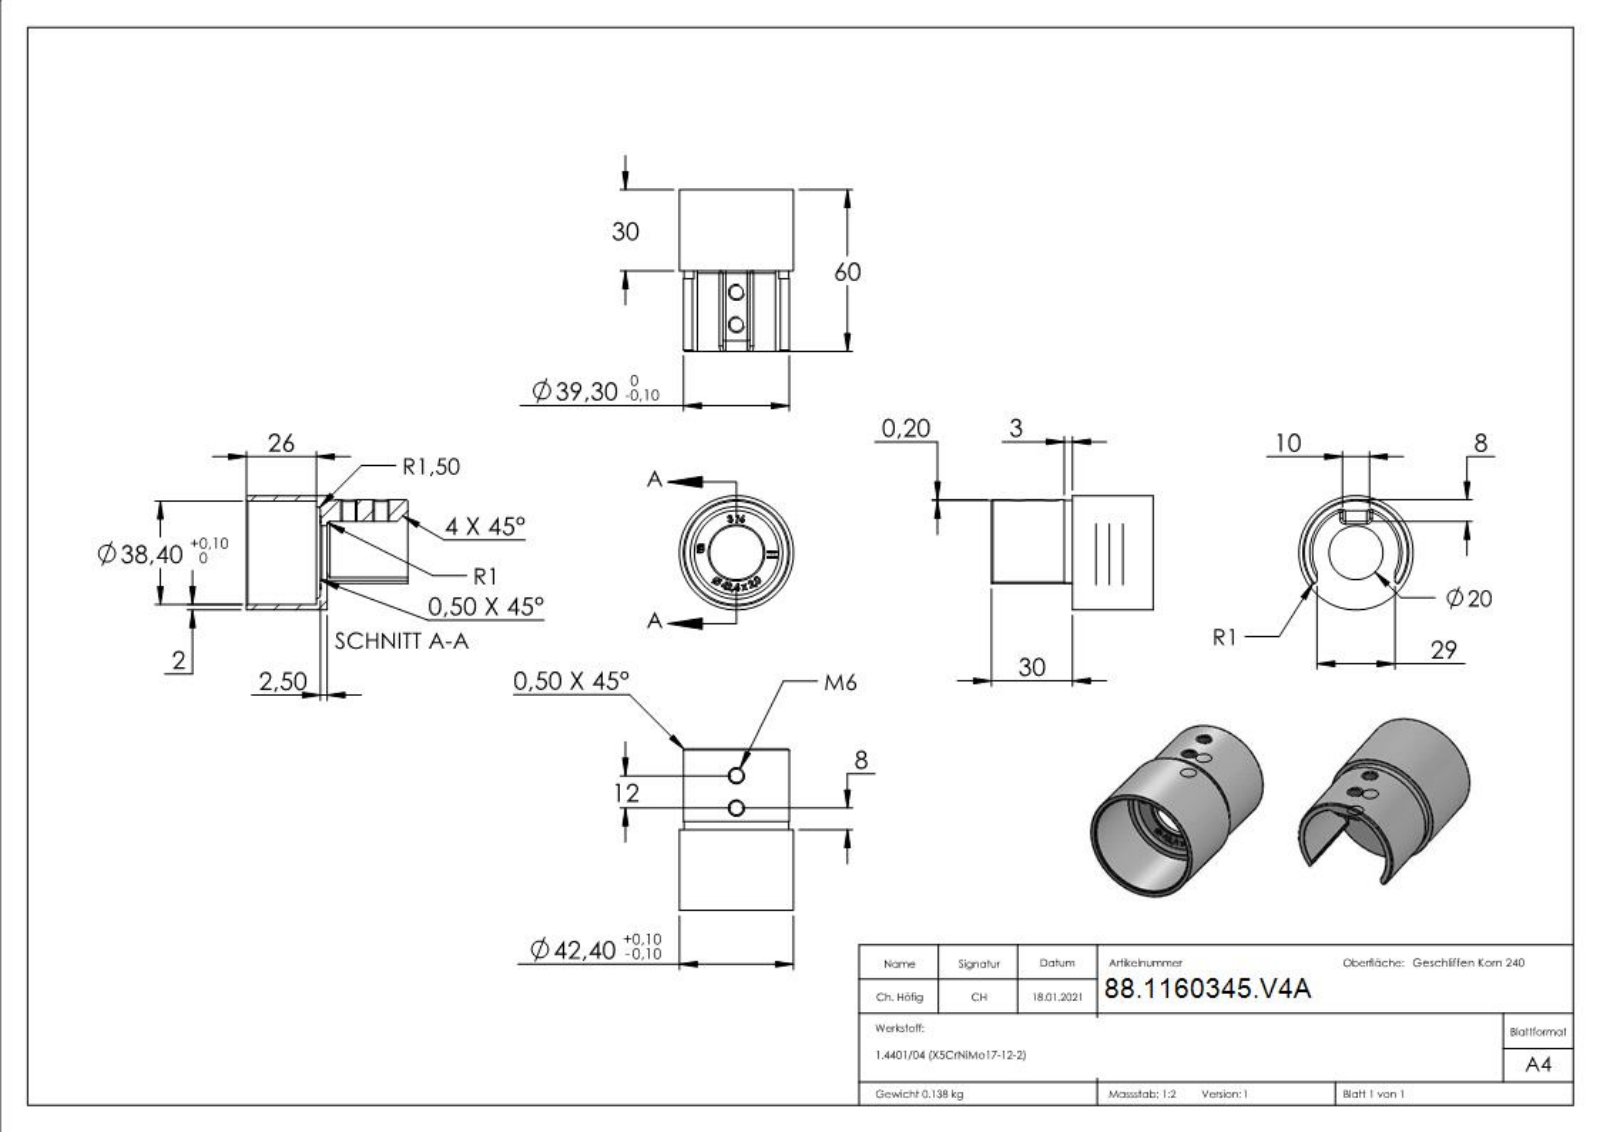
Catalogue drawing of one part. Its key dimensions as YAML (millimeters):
part_name: "60345-V4A"
step_written_by: "SolidWorks 2018 (CONFIG_CONTROL_DESIGN)"
units: millimeters
bodies: {solids: 1, faces: 487, planar: 272, cylindrical: 30, other: 185}
overall_size: [60, 42.4, 42.4]
volume: 17306
surface_area: 14805
round_holes:
  - {diameter: 5, count: 2}
  - {diameter: 20, count: 1}
  - {diameter: 38.4, count: 1}
round_bosses_or_shafts:
  - {diameter: 42.4, count: 1}
partial_cylinders:
  - {radius: 1, count: 11}
  - {radius: 17.15, count: 1}
  - {radius: 19.45, count: 1}
  - {radius: 19.65, count: 1}
face_to_face_distances: [2.5, 30, 4, 1.5, 27.5, 26, 32.5, 34, 60, 9.5]
hole_center_spacings: [12]
